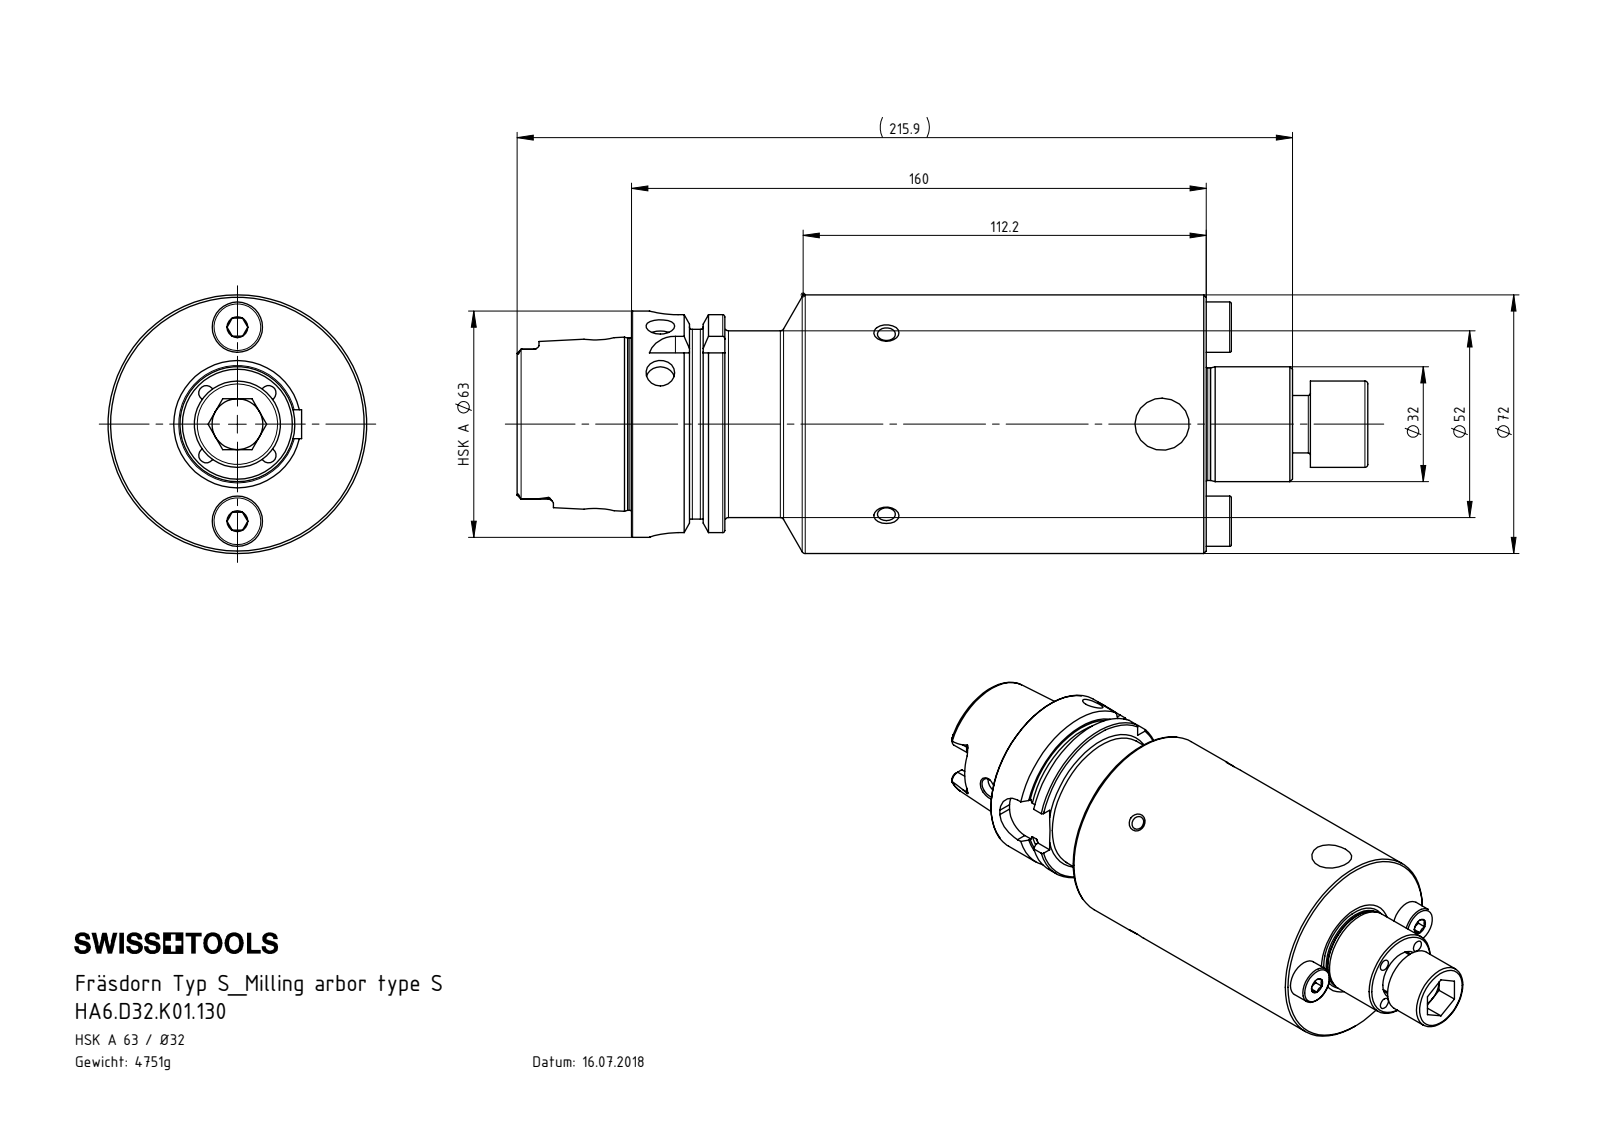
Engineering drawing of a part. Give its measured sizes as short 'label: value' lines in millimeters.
name: D32-ER2.001.022_C; D32-ER1.002.035_A; HA6-D32.K01.130_B_Fertigbearbeitung; DIN 6885 - 8x7x16 (+1 more)
written by: SolidWorks 2017 (AUTOMOTIVE_DESIGN)
unit: mm
bodies: 5 solids, 393 faces (96 planar, 120 cylindrical, 177 other)
size: 211.9 × 72 × 72
volume: 484 968 mm³; area: 65 409 mm²
holes: 6× ⌀4.2, 6× ⌀5, 2× ⌀8, 2× ⌀12, 1× ⌀7.5, 1× ⌀8.4, 1× ⌀10, 1× ⌀14, 1× ⌀17, 1× ⌀19, 1× ⌀34, 1× ⌀40
bosses: 2× ⌀14, 2× ⌀6, 2× ⌀4.6, 1× ⌀72, 1× ⌀63, 1× ⌀54.95, 1× ⌀52, 1× ⌀47.94
rounds: 6× R1.4, 4× R2.88, 4× R4, 4× R8
face distances: 130, 16, 25.95, 104.05, 9.95, 120.05, 154.05, 154, 144.05, 128.05
hole spacings: 12.25, 17.32, 20.28, 36.7, 49.05, 24.49, 27, 54
